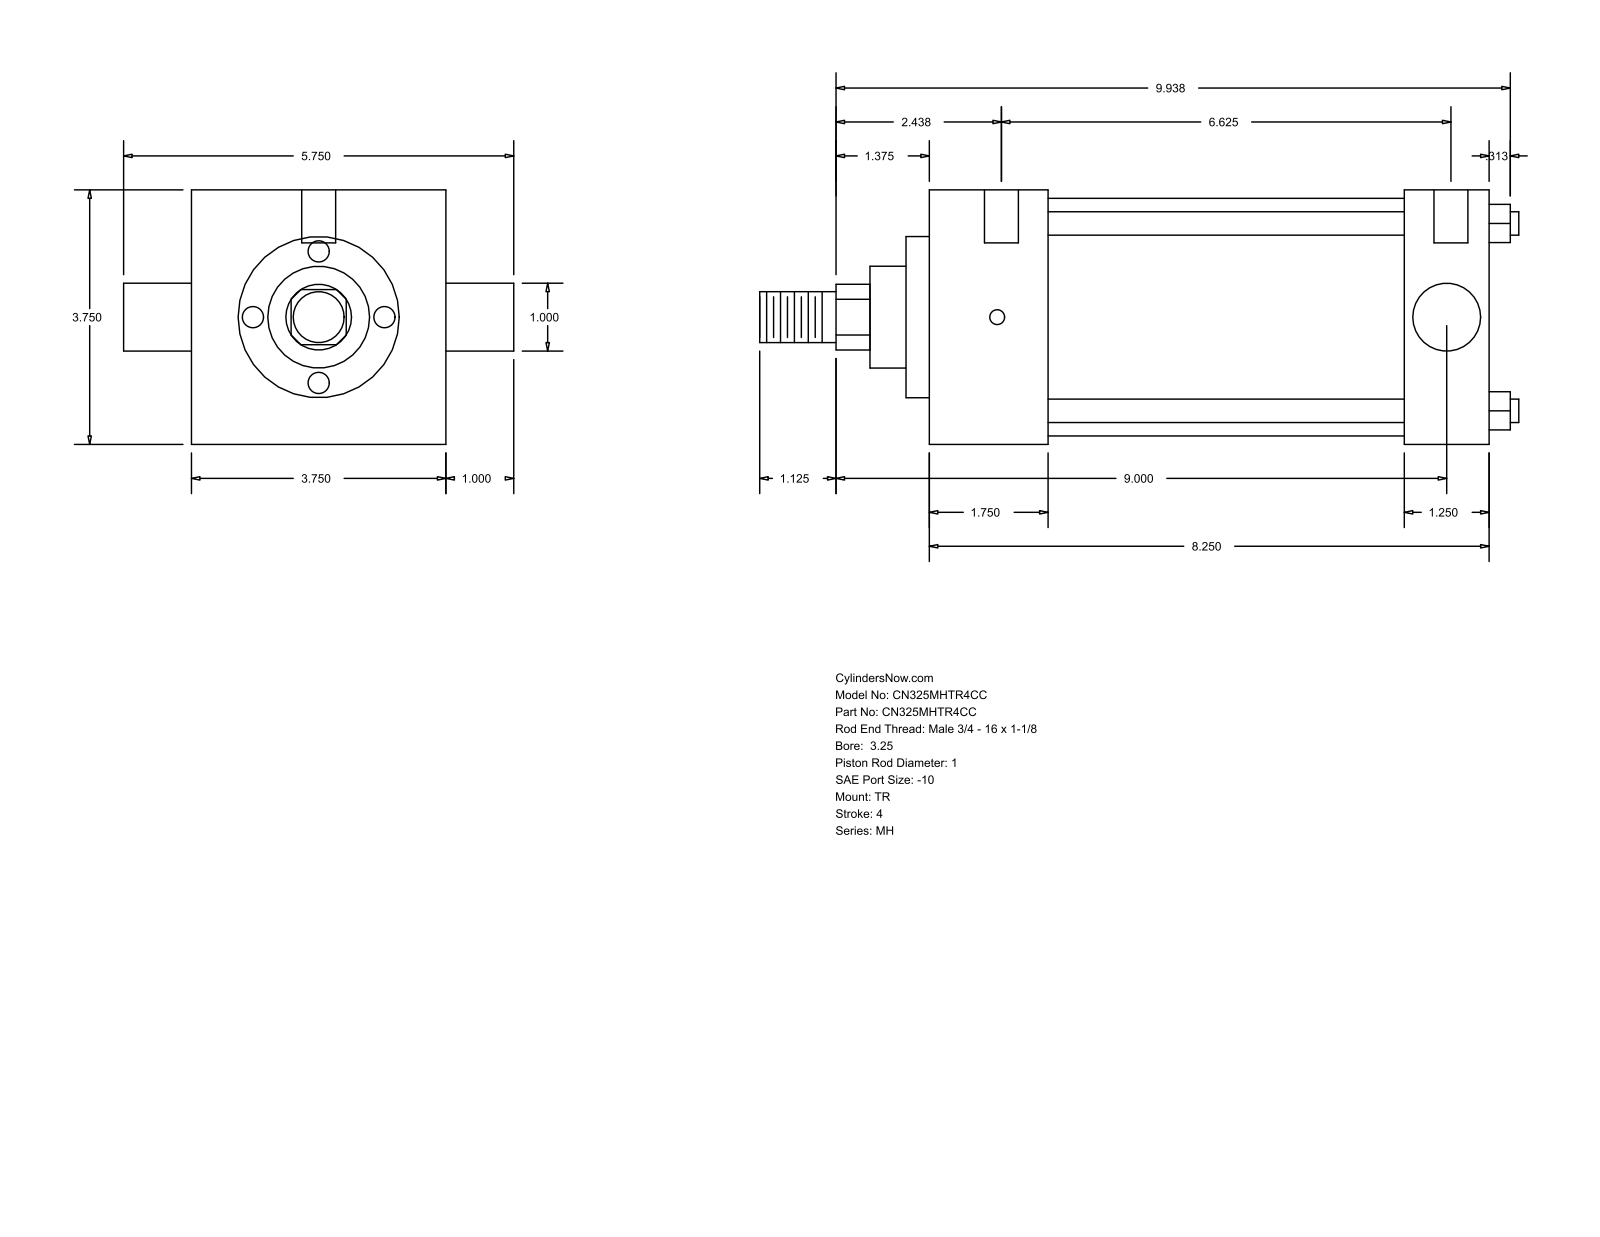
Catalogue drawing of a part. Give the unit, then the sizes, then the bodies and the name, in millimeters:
Units: millimetres
Overall size (bounding box): 284.16 × 146.05 × 95.25
Round holes (diameter × count): ⌀5.56 ×3, ⌀12.7 ×2
Round bosses / shafts (diameter × count): ⌀8.76 ×4, ⌀25.4 ×2, ⌀88.9 ×1, ⌀60.33 ×1, ⌀38.1 ×1, ⌀19.05 ×1
Partial cylindrical surfaces — rounded edges, fillets, slot ends (radius × count): R12.29 ×1
Main face-to-face distances: 95.24, 209.55, 44.46, 177.8, 133.34, 165.09, 31.75, 8.73, 53.19, 186.53
Hole centre spacings: 1.58, 4.76, 168.28, 169.86, 173.04, 174.62
Bodies: 0 solids, 86 faces (61 planar, 25 cylindrical, 0 other)
Part name (STEP PRODUCT): MH_TR__0325_1
STEP written by: GSSL Pune (CONFIG_CONTROL_DESIGN)
